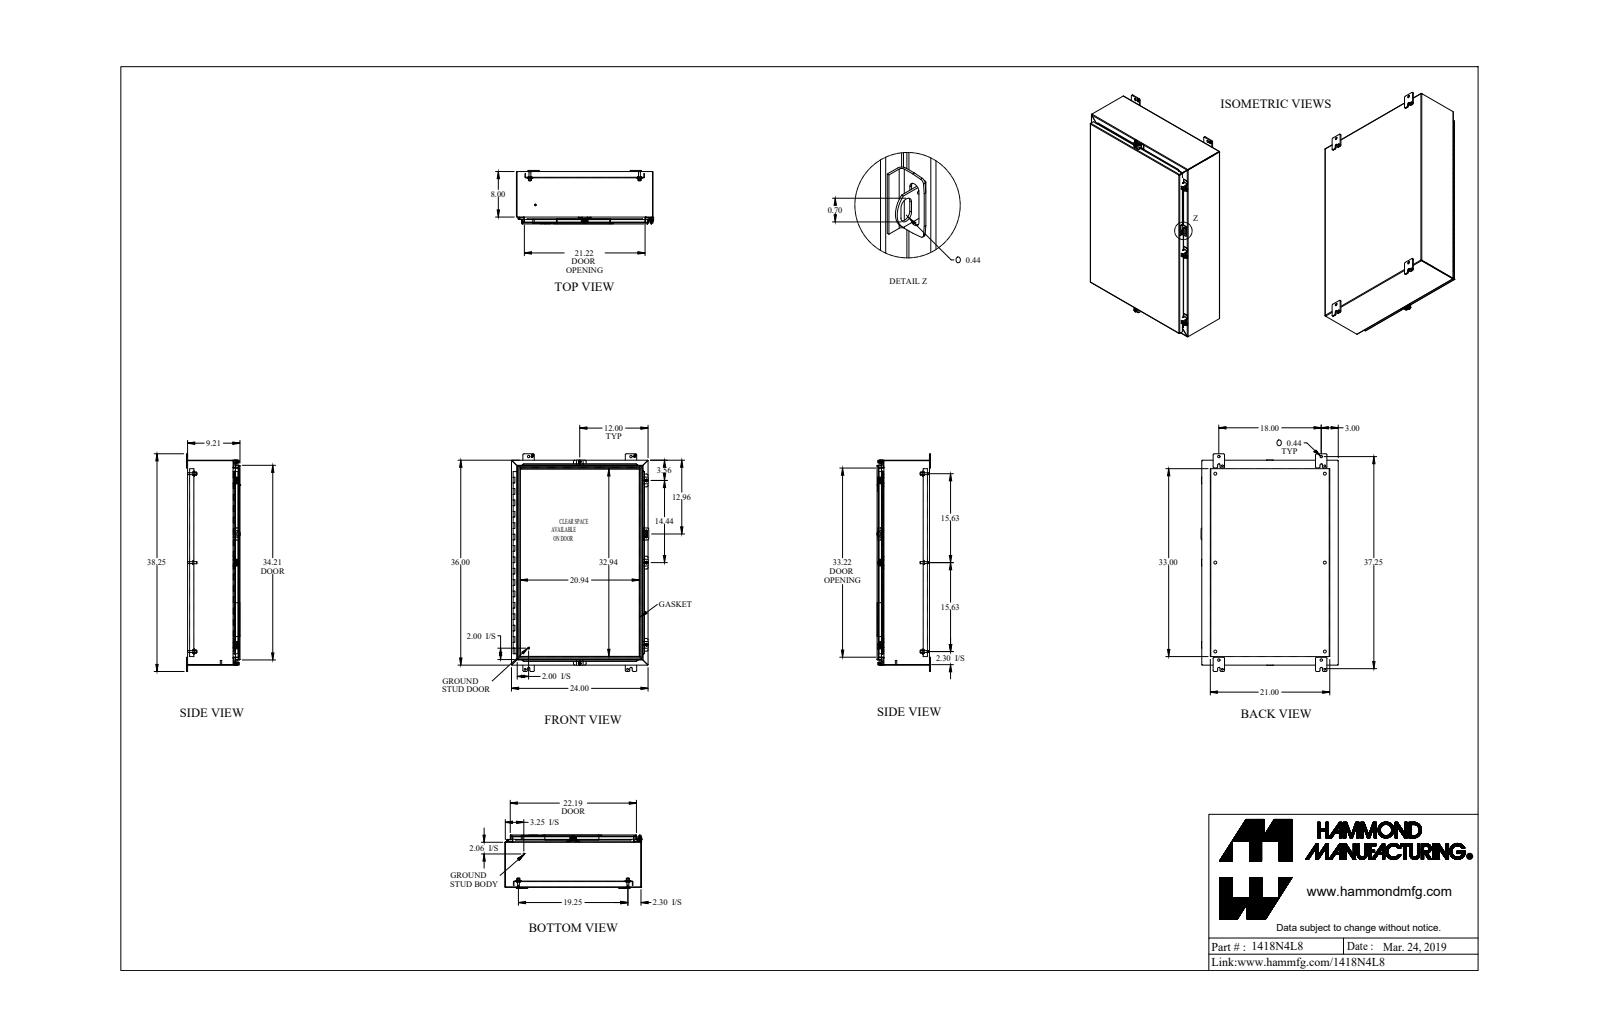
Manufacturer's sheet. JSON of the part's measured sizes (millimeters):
{"part_name": "1418N4L8_Default", "step_written_by": "SolidWorks 2019 (CONFIG_CONTROL_DESIGN)", "units": "millimeters", "bodies": {"solids": 49, "faces": 1727, "planar": 1017, "cylindrical": 608, "other": 102}, "overall_size": [971.6, 612.8, 239.7], "volume_mm3": 4988000, "surface_area_mm2": 5123000, "round_holes": [[12.7, 6], [5.4, 5], [9.5, 5], [6.7, 4], [7.8, 4], [8, 4], [11.1, 4], [11.3, 4], [3.2, 1], [4.7, 1], [6.7, 1]], "round_bosses_or_shafts": [[16.5, 6], [9.5, 6], [8.4, 6], [12.7, 5], [9.9, 5], [6.2, 5], [25.4, 4], [7.1, 2]], "partial_cylinders_radius": [[1.2, 27], [3.6, 27], [4.8, 26], [0.9, 24], [2.7, 24], [6.4, 24], [3.2, 10], [3.6, 10]], "face_to_face_distances": [1.8, 1.8, 230.3, 232.1, 232.1, 233.9, 205.9, 204.1, 26.2, 28], "hole_center_spacings": [489, 793.8, 932.3, 250.4, 250.4, 396.9, 396.9, 629.7]}
